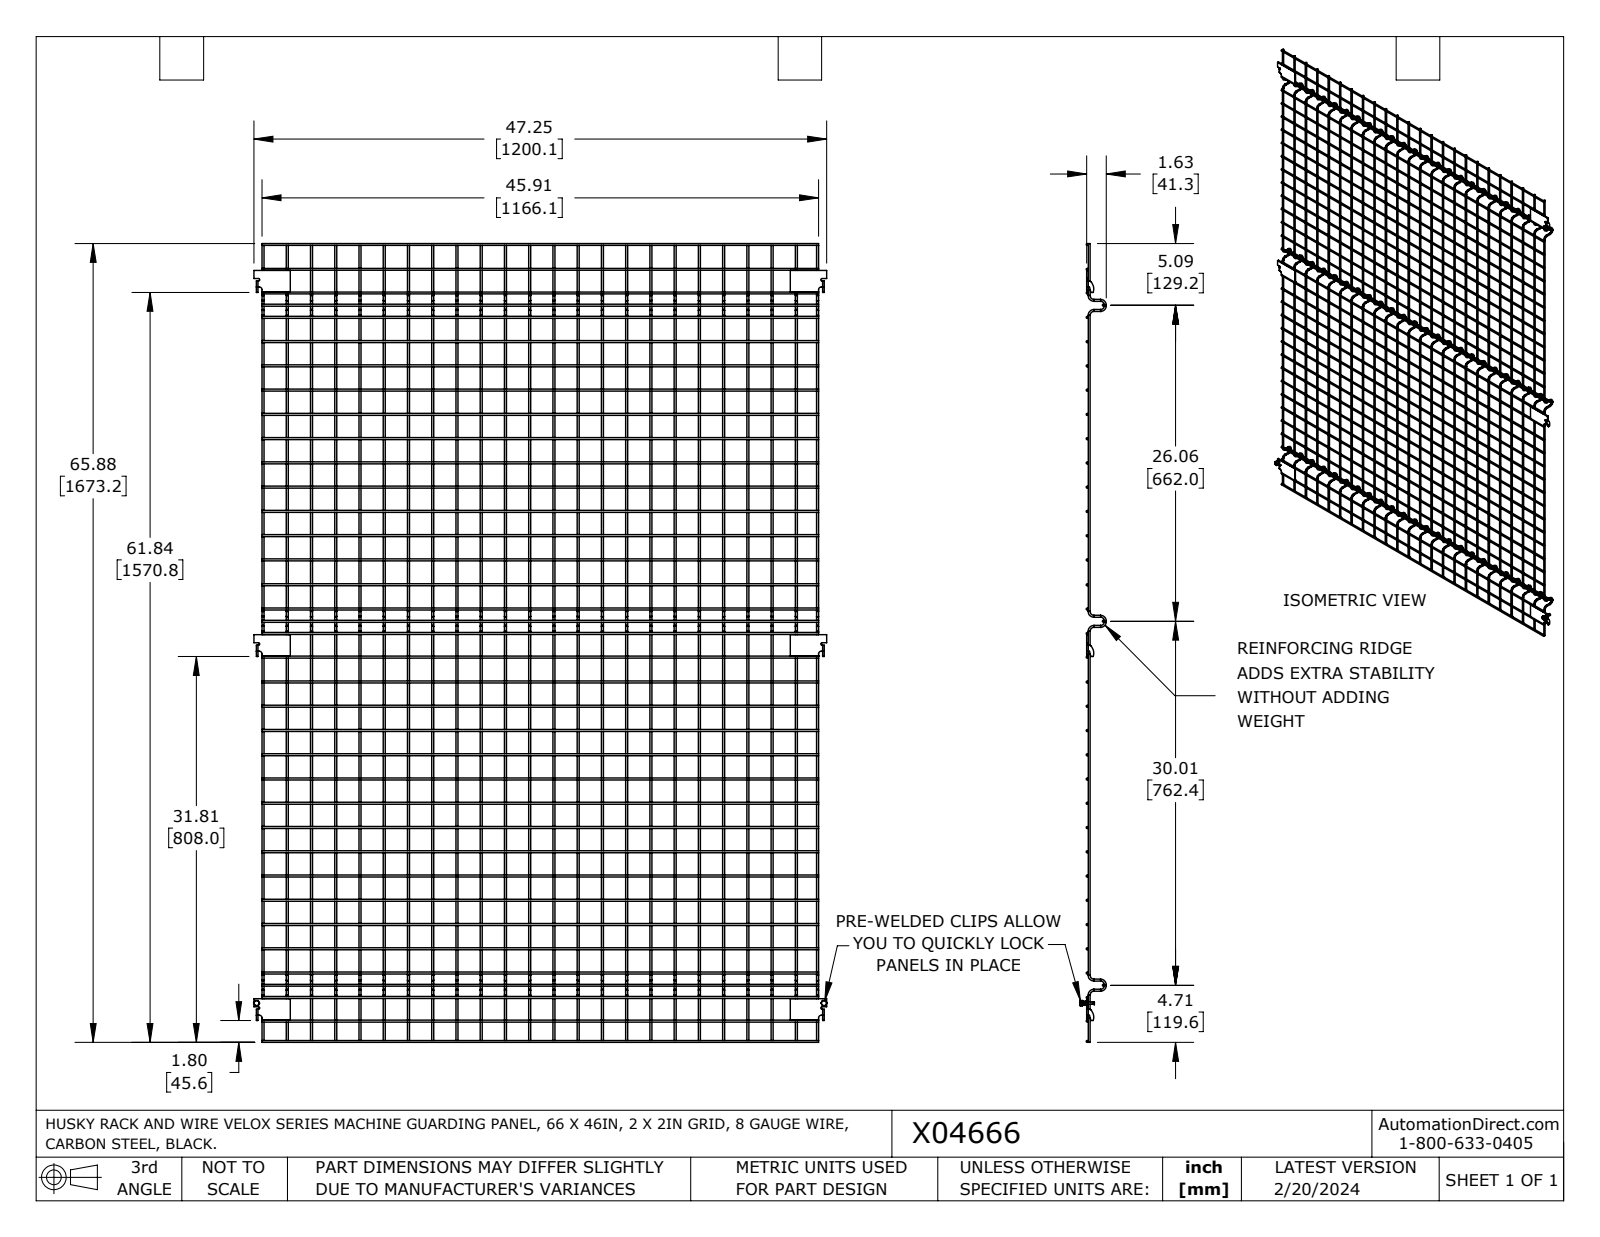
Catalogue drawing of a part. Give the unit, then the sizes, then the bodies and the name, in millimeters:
Units: millimetres
Overall size (bounding box): 1673.2 × 1201.8 × 53.4
Round holes (diameter × count): ⌀5.1 ×2, ⌀6.4 ×2
Round bosses / shafts (diameter × count): ⌀4.1 ×229, ⌀9.9 ×2, ⌀6.2 ×2, ⌀4.7 ×2
Partial cylindrical surfaces — rounded edges, fillets, slot ends (radius × count): R2.5 ×6, R5.5 ×6, R6.4 ×3, R22 ×3, R0.2 ×2, R1.7 ×2, R3.4 ×2
Main face-to-face distances: 3.4, 3.2, 44.8, 11.9, 1178, 1525.2, 762.8, 71.1, 1118.8, 59.2
Hole centre spacings: 1188.9
Volume: 1 196 000 mm³ · Surface area: 1 159 000 mm²
Bodies: 71 solids, 939 faces (230 planar, 397 cylindrical, 312 other)
Part name (STEP PRODUCT): X04666
STEP written by: SolidWorks 2023 (AUTOMOTIVE_DESIGN)
